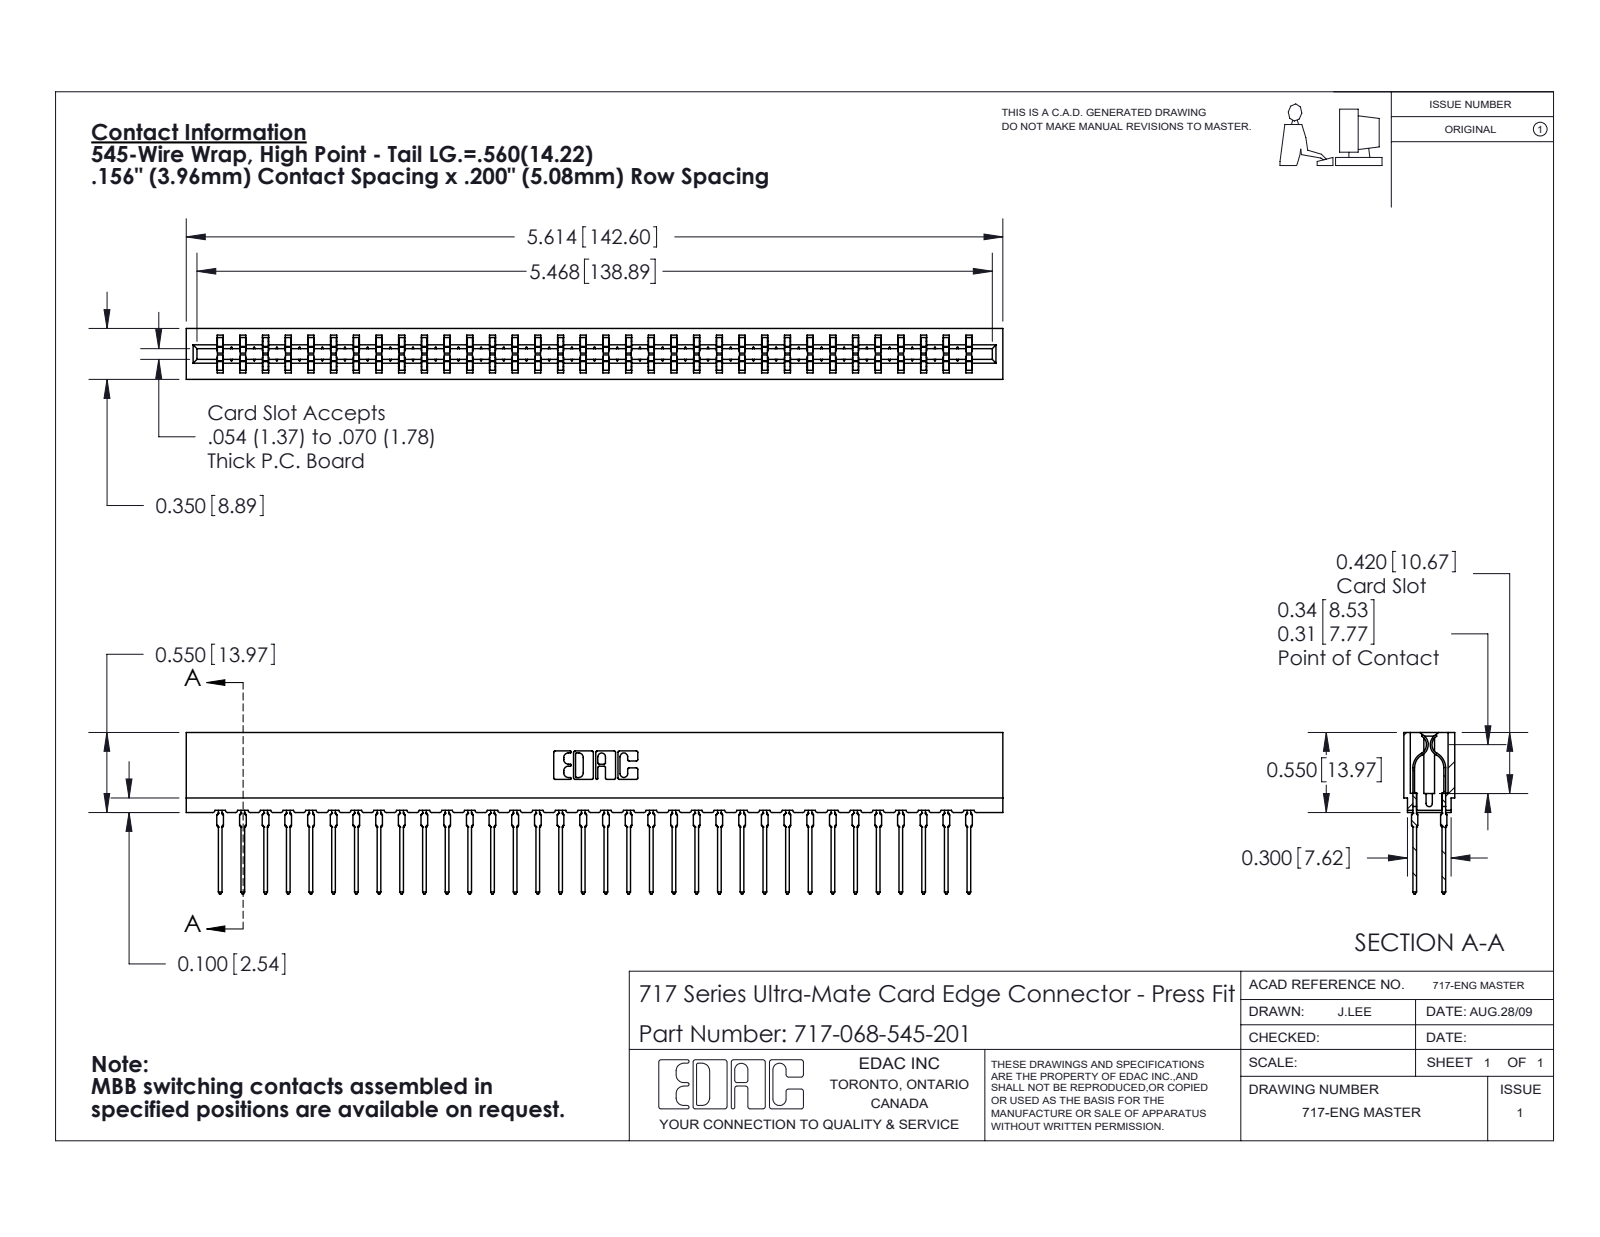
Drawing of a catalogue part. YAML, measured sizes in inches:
part_name: "717 Part_Insulator Option - 06; 717-068-545-201; 745-292-001_545"
step_written_by: "SolidWorks 2020 (CONFIG_CONTROL_DESIGN)"
units: inches
bodies: {solids: 69, faces: 6214, planar: 3216, cylindrical: 1230, other: 1768}
overall_size: [5.614, 1.109, 0.35]
volume: 0.771
surface_area: 31.56
partial_cylinders:
  - {radius: 0.021, count: 136}
  - {radius: 0.015, count: 68}
  - {radius: 0.01, count: 22}
  - {radius: 0.005, count: 8}
  - {radius: 0.011, count: 8}
  - {radius: 0.007, count: 6}
  - {radius: 0.031, count: 6}
  - {radius: 0.026, count: 3}
face_to_face_distances: [0.212, 0.138, 0.35, 0.063, 0.287, 0.076, 0.149, 0.074, 0.087, 0.263]
